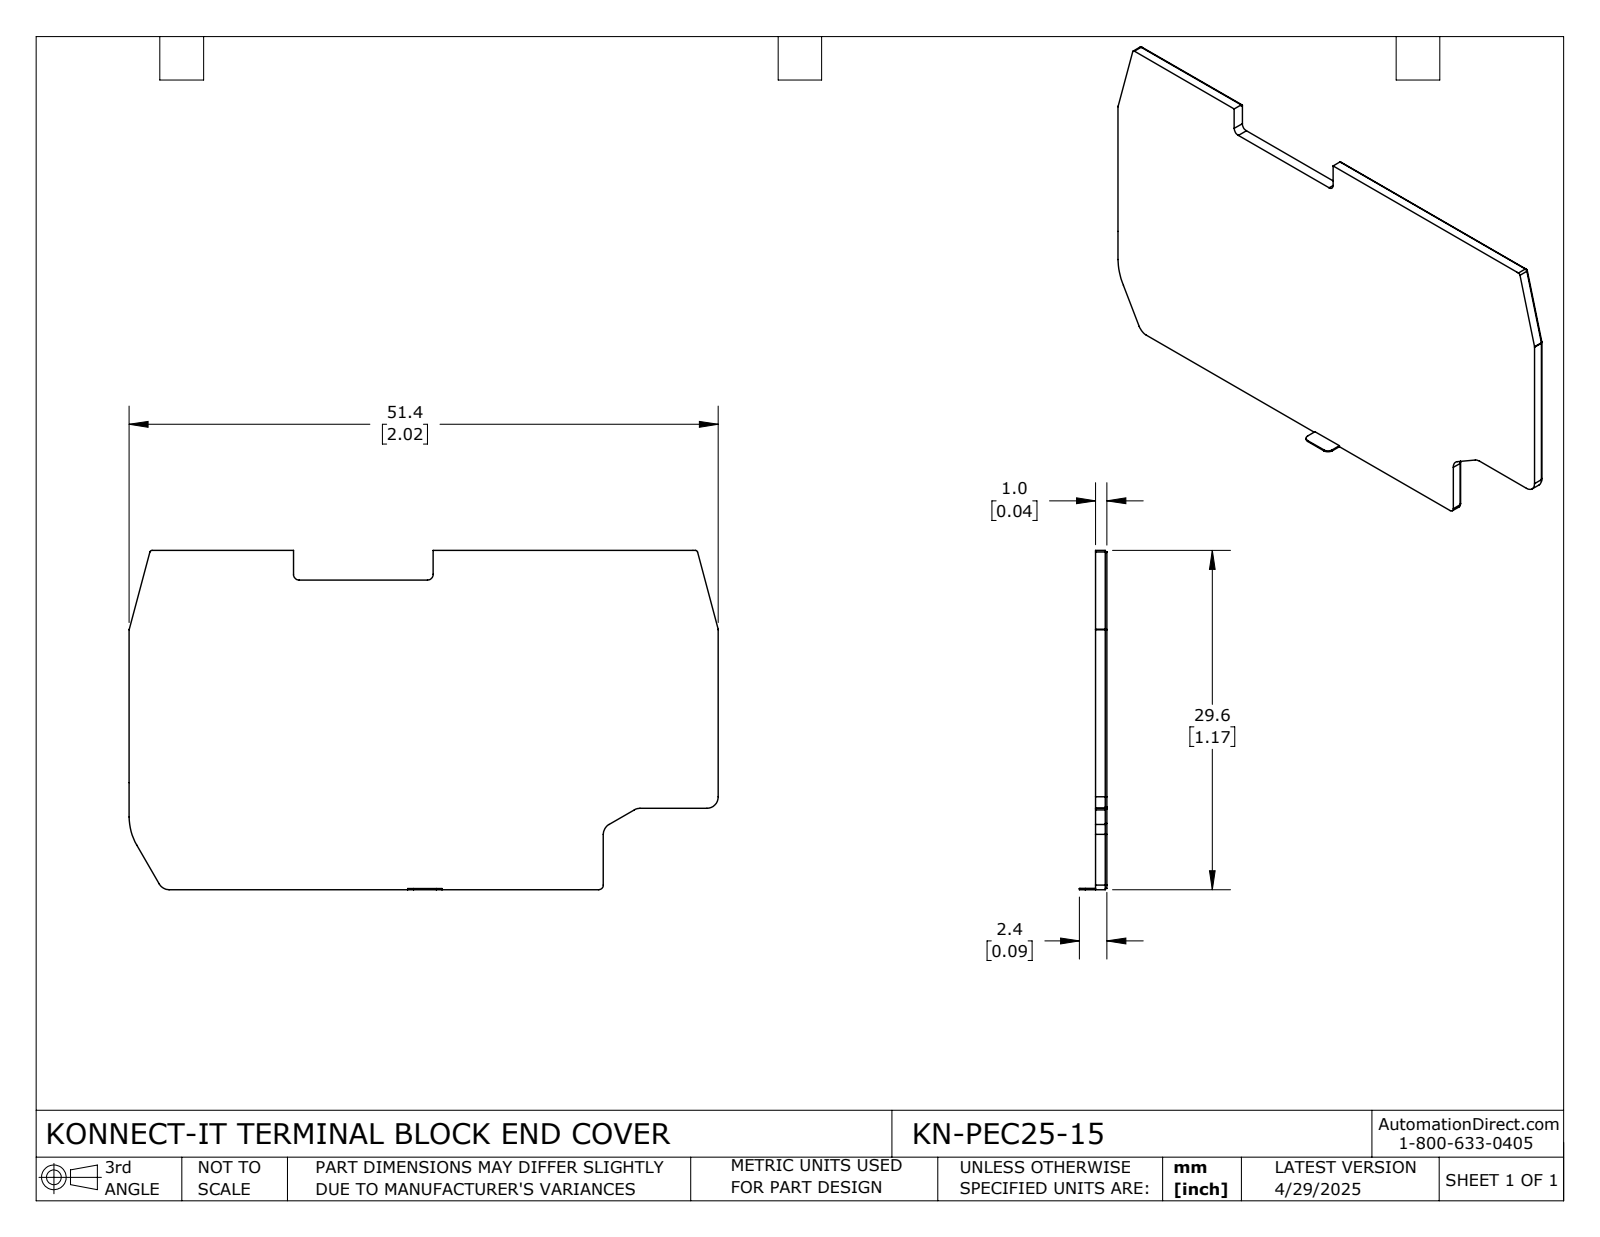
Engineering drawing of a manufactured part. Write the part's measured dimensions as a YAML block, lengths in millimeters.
part_name: "KN-PEC25-15"
step_written_by: "SolidWorks 2024 (CONFIG_CONTROL_DESIGN)"
units: millimeters
bodies: {solids: 1, faces: 56, planar: 32, cylindrical: 24, other: 0}
overall_size: [51.43, 29.61, 2.4]
volume: 1400
surface_area: 2972
partial_cylinders:
  - {radius: 0.1, count: 4}
  - {radius: 0.2, count: 4}
  - {radius: 0.5, count: 4}
  - {radius: 1, count: 4}
  - {radius: 0.9, count: 2}
  - {radius: 1.1, count: 2}
  - {radius: 0.3, count: 1}
  - {radius: 0.4, count: 1}
face_to_face_distances: [1, 29.61, 29.51, 0.85, 51.43, 27.02, 2.59, 26.92, 7.1, 22.41]
